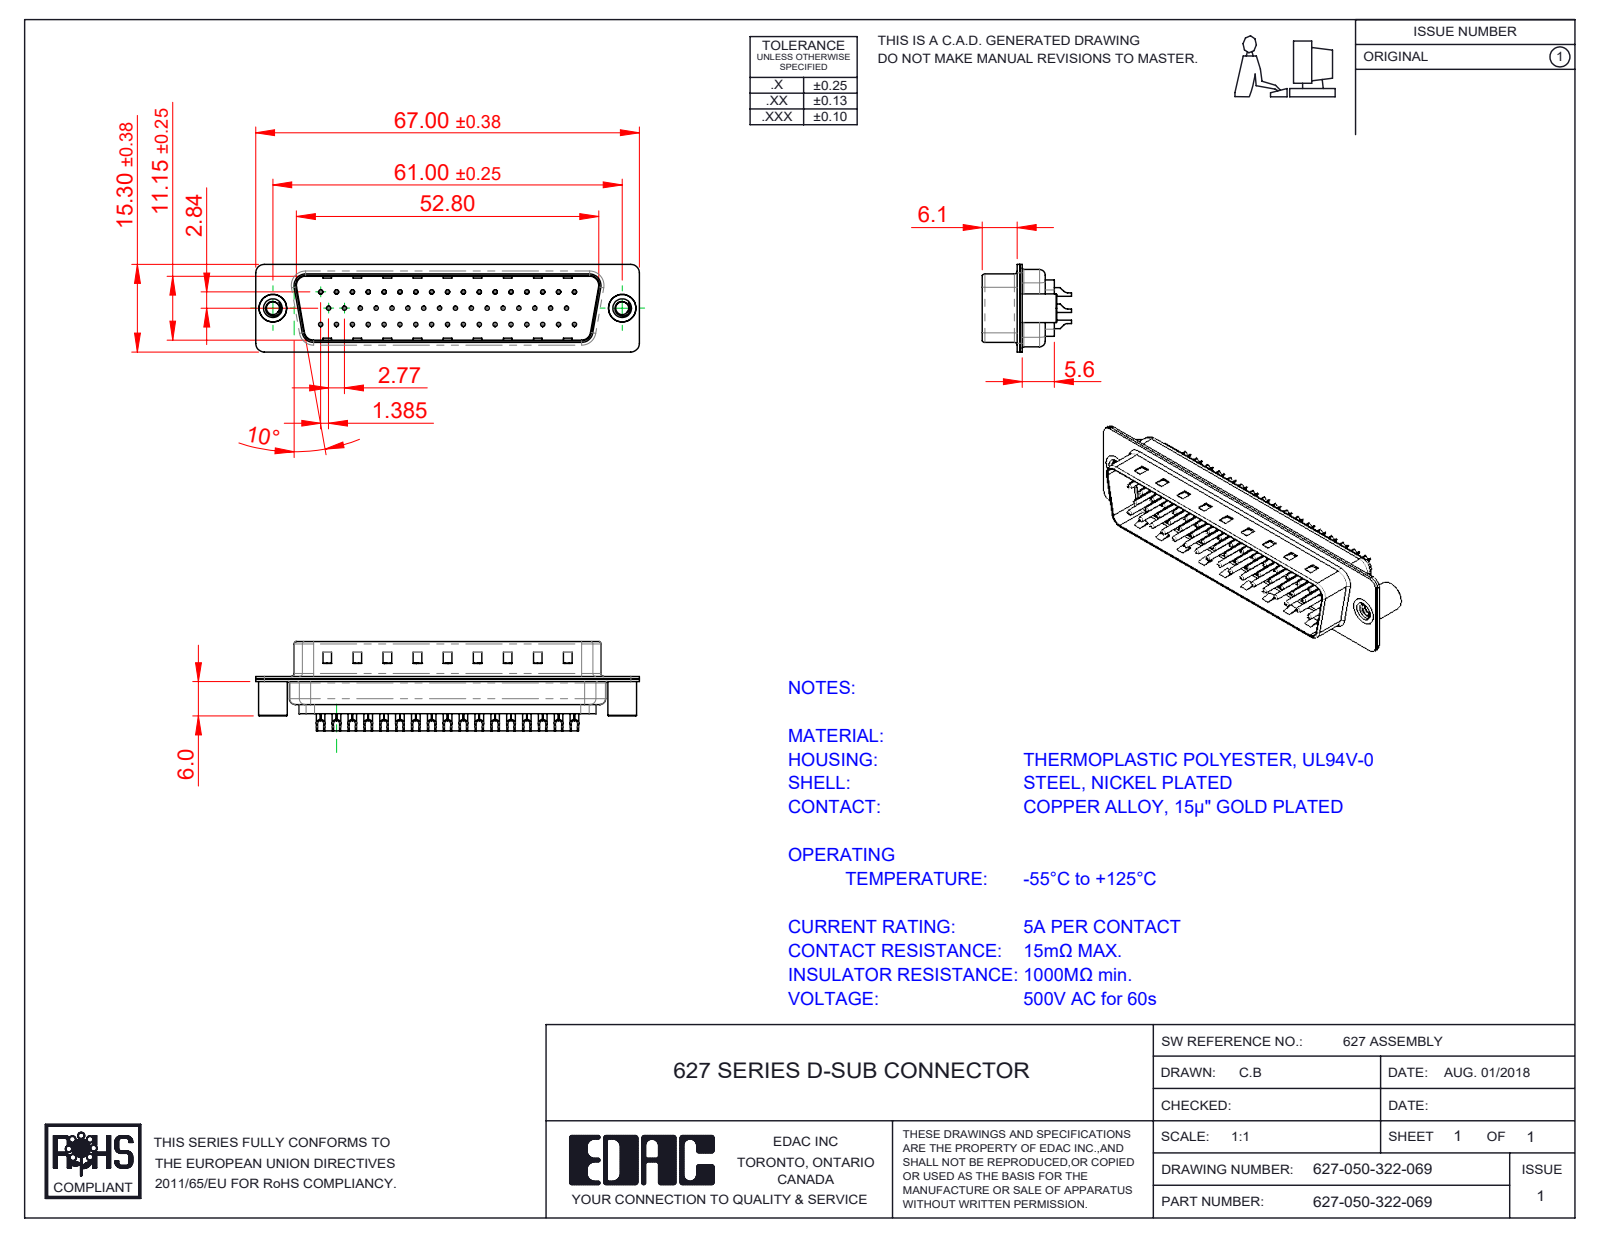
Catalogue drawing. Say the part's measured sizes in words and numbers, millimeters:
The part is named "627 Shell Front_50 Contacts; 627 Contact Row 2_22M; 627 Contact Row 1_22L; 627 4-40 Threaded Standoff BS (+4 more)". Its 3-D file was written by "SolidWorks 2020 (CONFIG_CONTROL_DESIGN)". It is 55 solids with 3634 faces: 903 planar, 1611 cylindrical and 1120 other. Overall it measures 67 by 15.6 by 15.3 millimeters. Its volume is 4 548 cubic millimeters and its surface area 12 964 square millimeters. Round holes: 58 of diameter 1.6, 50 of diameter 0.35, 50 of diameter 1.1, 8 of diameter 0.75, 8 of diameter 2, 2 of diameter 2.26, 2 of diameter 4, 2 of diameter 4.8. Round bosses or shafts: 50 of diameter 2, 50 of diameter 1.5, 50 of diameter 0.75, 2 of diameter 5, 2 of diameter 4.9. Partial cylindrical surfaces (rounded edges, fillets, slot ends): 16 of radius 1.5, 12 of radius 2, 8 of radius 0.5, 8 of radius 1.6, 7 of radius 1, 4 of radius 0.25, 4 of radius 0.6, 4 of radius 0.65. The main face-to-face distances are 0.4, 0.45, 11.55, 0.9, 6.05, 6.5, 0.78, 1.95, 0.77, 12.33. The hole center spacings are 2.77, 3.16, 5.54, 8.31, 11.08, 13.85, 16.62, 19.39.
